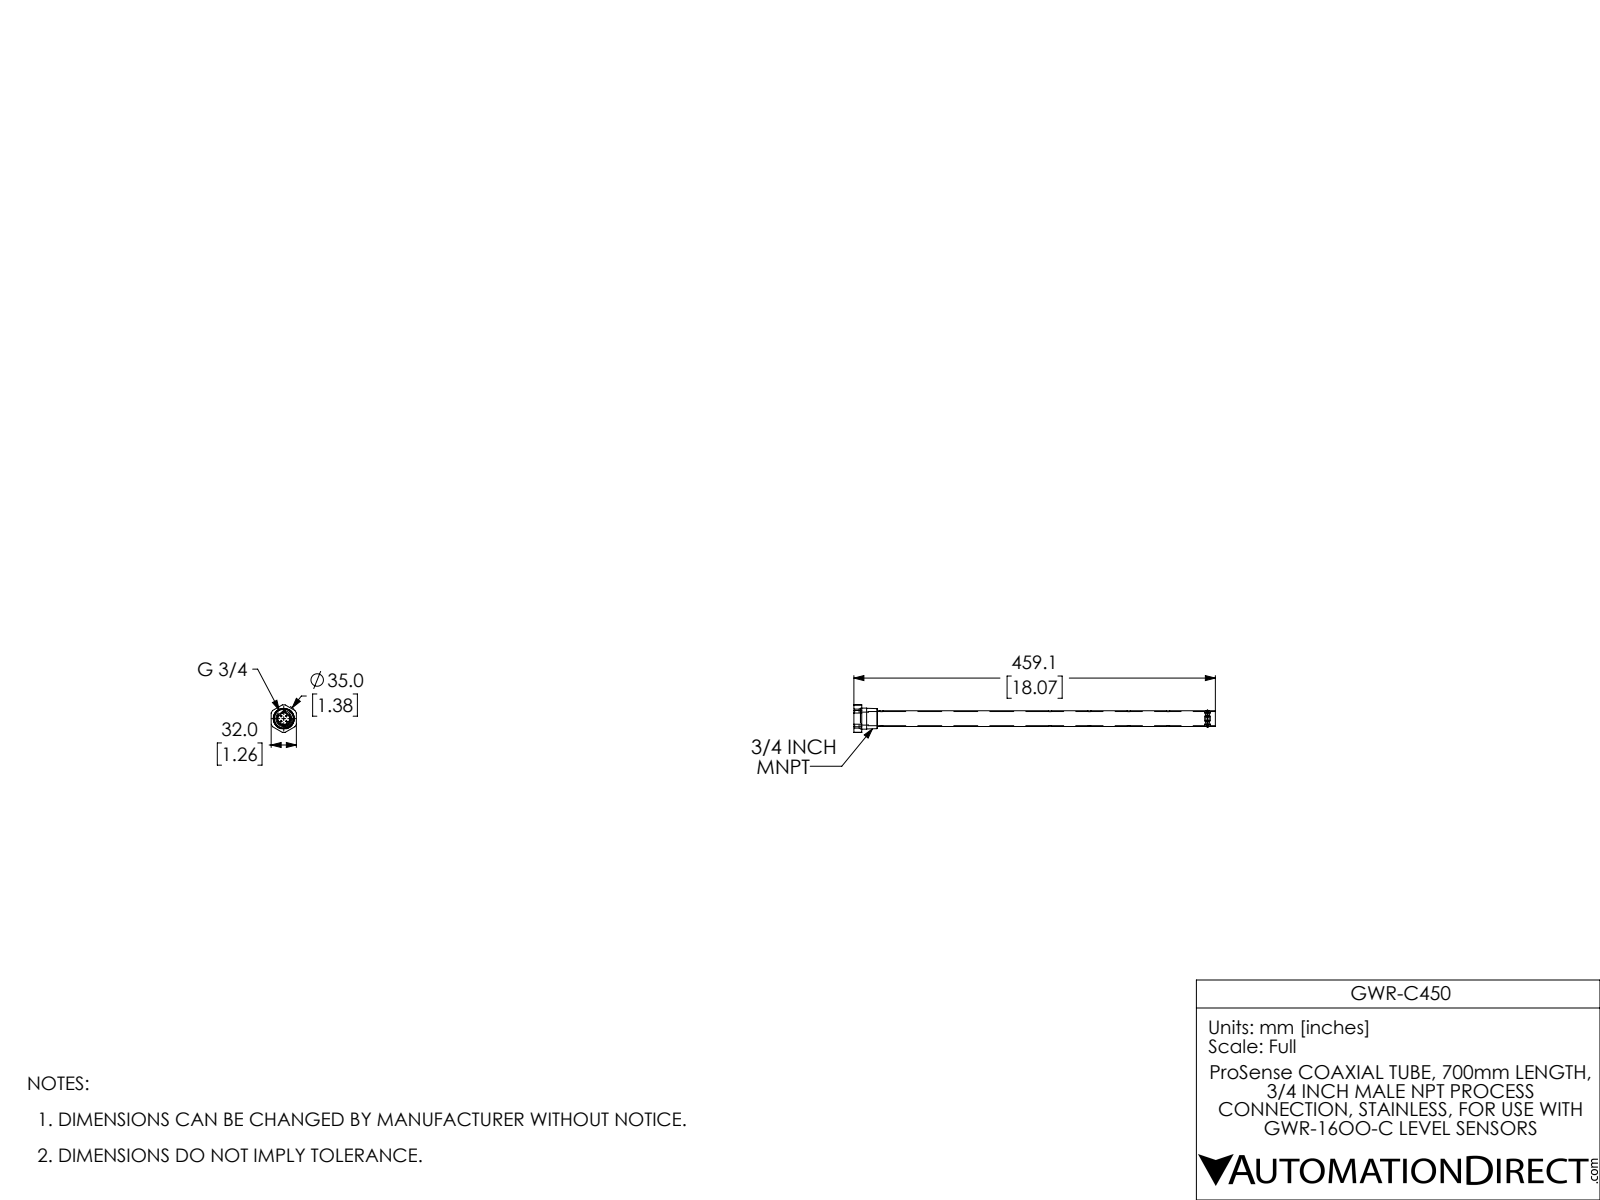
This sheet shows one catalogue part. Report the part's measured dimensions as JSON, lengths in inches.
{"part_name": "GWR-C450", "step_written_by": "SolidWorks 2017 (AUTOMOTIVE_DESIGN)", "units": "inches", "bodies": {"solids": 1, "faces": 134, "planar": 24, "cylindrical": 86, "other": 24}, "overall_size": [18.075, 1.378, 1.26], "volume_in3": 2.21, "surface_area_in2": 89.04, "round_holes": [[0.157, 6], [0.65, 1], [0.709, 1], [0.95, 1]], "round_bosses_or_shafts": [[0.039, 2], [1.053, 1], [0.787, 1]], "partial_cylinders_radius": [[0.075, 8], [0.159, 1], [0.276, 1], [0.295, 1], [0.39, 1], [0.689, 1]], "face_to_face_distances": [1.26, 0.394, 0.035, 0.358, 0.787, 0.823, 1.181, 16.523, 17.31, 17.346], "hole_center_spacings": [1.969, 3.937, 5.906, 7.874, 8.425, 10.394, 12.362, 14.331]}
